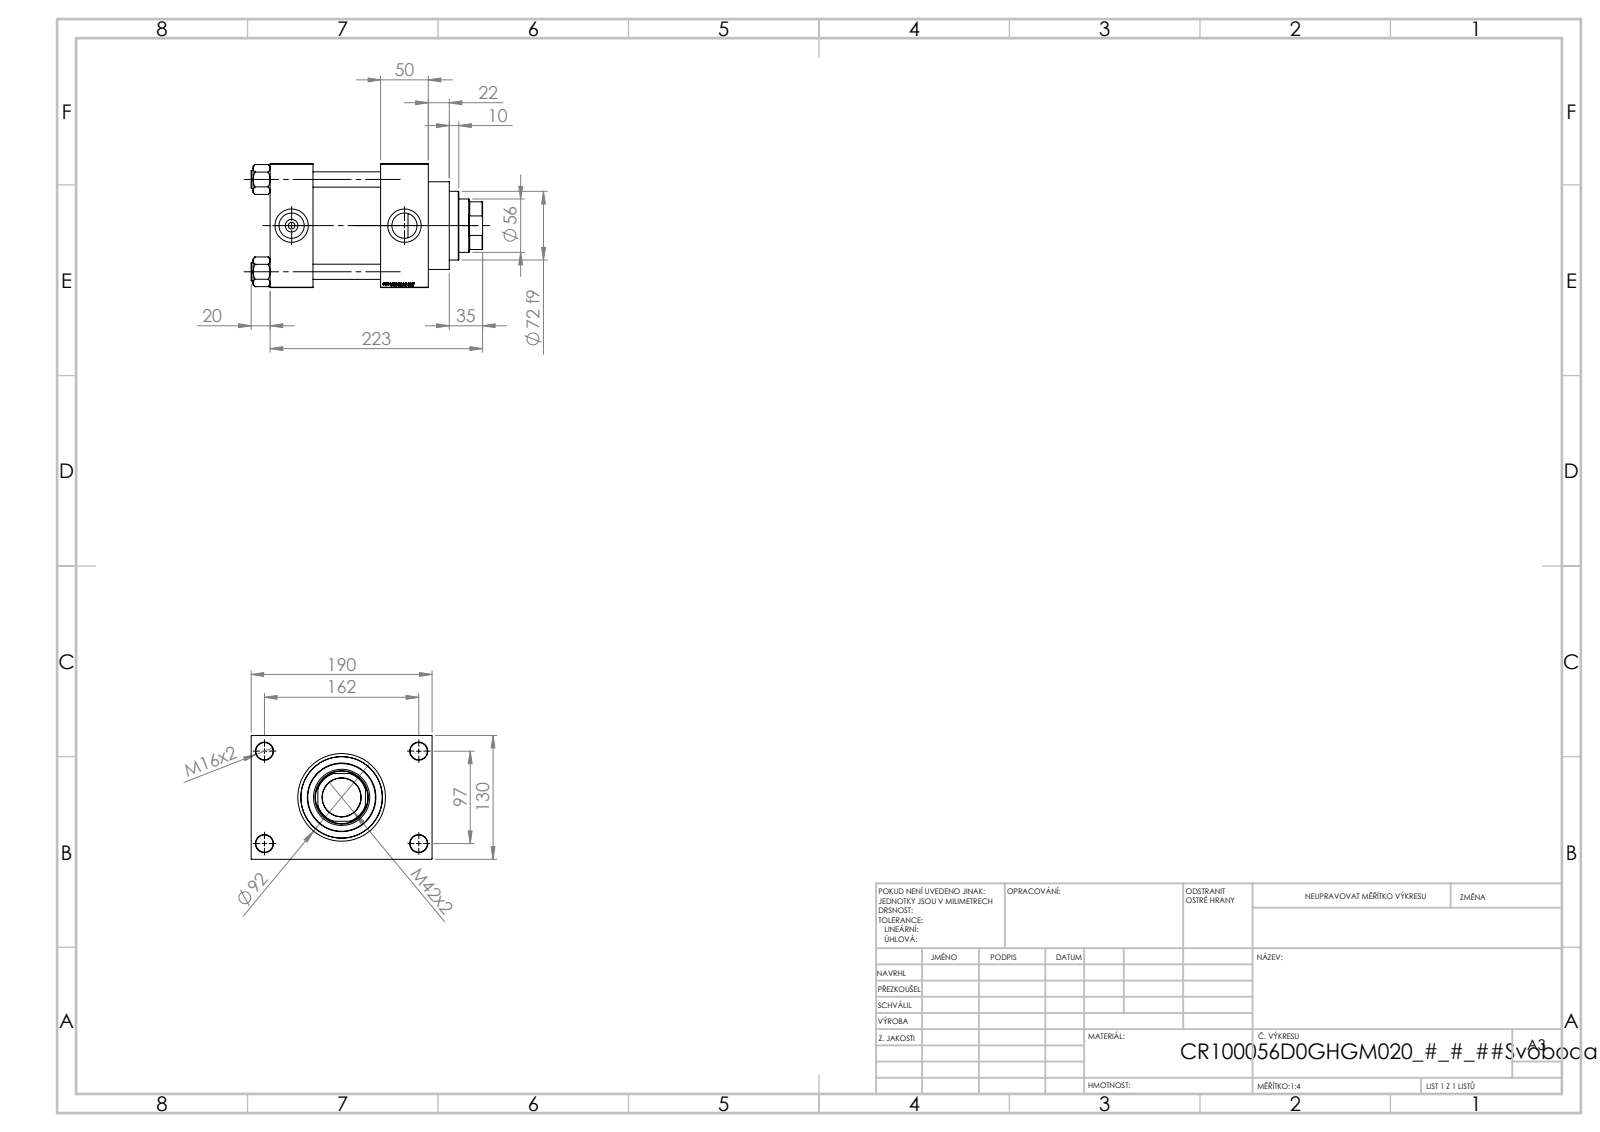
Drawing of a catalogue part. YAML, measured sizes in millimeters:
part_name: "NUT_M5_D; V215CR_D_TYCINKA; V215CR_D_Body; V215_VC_A (+1 more)"
step_written_by: "SolidWorks 2019 (CONFIG_CONTROL_DESIGN)"
units: millimeters
bodies: {solids: 11, faces: 1151, planar: 545, cylindrical: 88, other: 518}
overall_size: [243, 190, 130]
volume: 2628000
surface_area: 362363
round_holes:
  - {diameter: 16, count: 4}
  - {diameter: 18, count: 4}
  - {diameter: 7, count: 2}
  - {diameter: 26.44, count: 2}
  - {diameter: 35, count: 2}
  - {diameter: 40.5, count: 1}
  - {diameter: 56, count: 1}
  - {diameter: 59, count: 1}
  - {diameter: 76, count: 1}
  - {diameter: 85.5, count: 1}
  - {diameter: 100, count: 1}
round_bosses_or_shafts:
  - {diameter: 19, count: 4}
  - {diameter: 106, count: 1}
  - {diameter: 92, count: 1}
  - {diameter: 72, count: 1}
partial_cylinders:
  - {radius: 27, count: 1}
face_to_face_distances: [130, 116, 50, 45, 71, 121, 166, 30, 160, 20]
hole_center_spacings: [32.55, 68.52, 94.41, 96.9, 102.27, 129.45, 161.73, 97]
